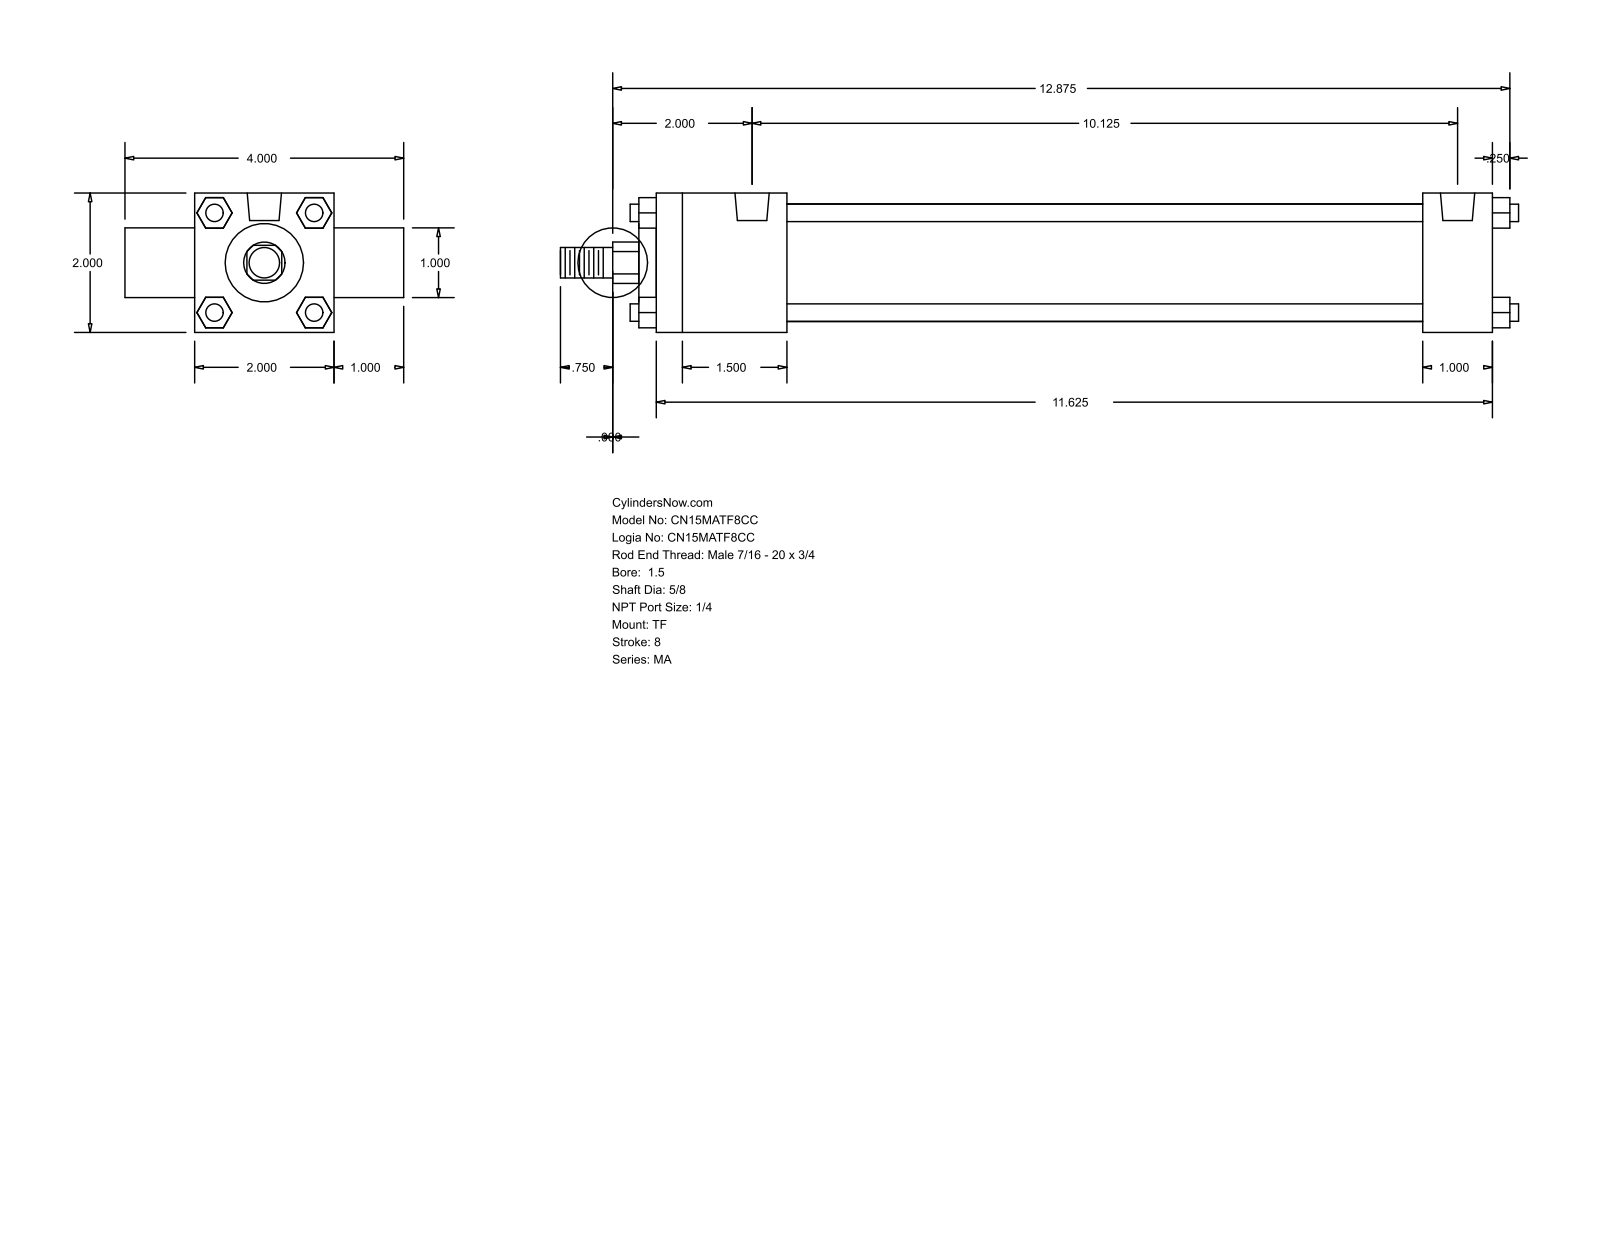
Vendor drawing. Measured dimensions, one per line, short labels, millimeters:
name: MA_TF__0150_0.625
written by: GSSL Pune (CONFIG_CONTROL_DESIGN)
unit: mm
bodies: 0 solids, 120 faces (92 planar, 28 cylindrical, 0 other)
size: 349.25 × 101.6 × 50.8
holes: 3× ⌀7.94, 2× ⌀12.49
bosses: 4× ⌀6.35, 1× ⌀42.93, 1× ⌀28.57, 1× ⌀25.4, 1× ⌀15.88, 1× ⌀11.11
rounds: 1× R7.54
face distances: 50.8, 304.8, 25.4, 76.2, 47.62, 279.39, 231.77, 257.18, 25.41, 6.35
hole spacings: 257.18
